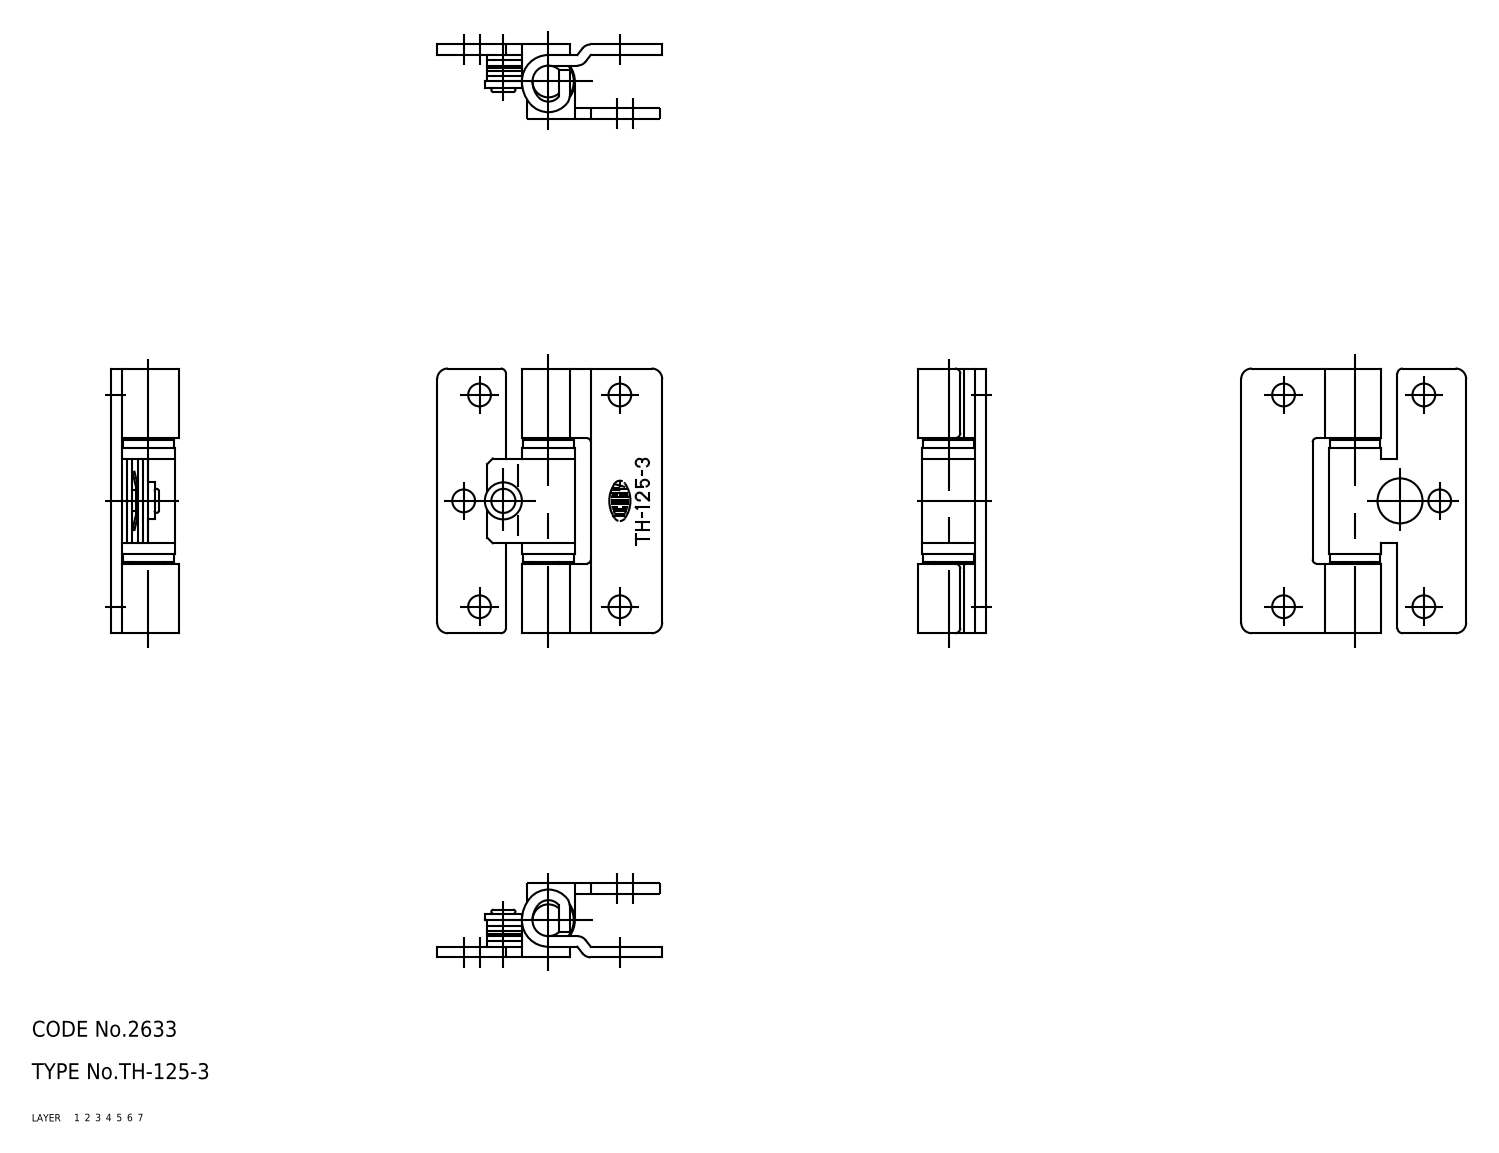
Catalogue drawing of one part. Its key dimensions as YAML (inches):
part_name: "washer_2; washer_1; spacer; shaft (+5 more)"
step_written_by: "CADfix (AUTOMOTIVE_DESIGN)"
units: inches
bodies: {solids: 10, faces: 164, planar: 0, cylindrical: 0, other: 164}
overall_size: [1.969, 1.673, 0.504]
volume: 0.46
surface_area: 15.94
